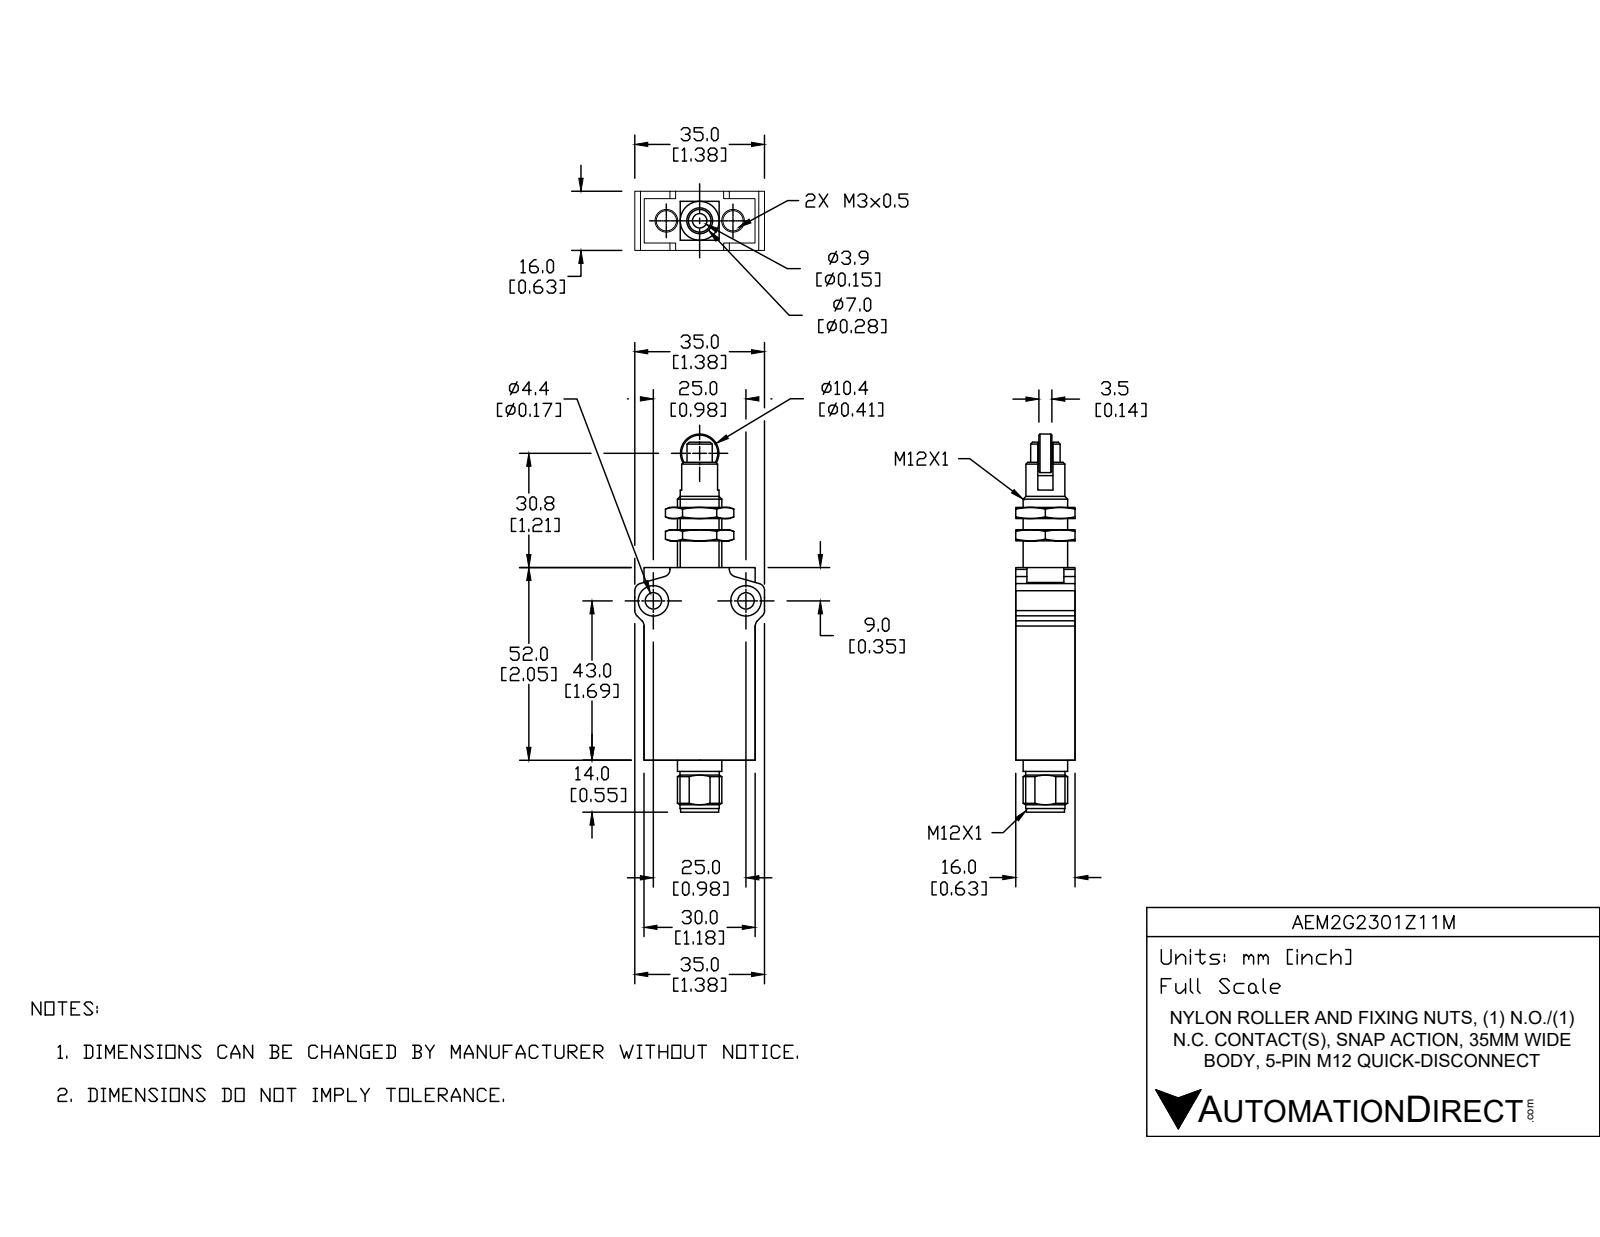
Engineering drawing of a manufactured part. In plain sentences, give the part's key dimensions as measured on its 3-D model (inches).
The part is named "AEM2G2301Z11M". Its 3-D file was written by "SolidWorks 2017 (AUTOMOTIVE_DESIGN)". It is 6 solids with 229 faces: 82 planar, 76 cylindrical and 71 other. Overall it measures 4.016 by 1.378 by 0.63 inches. Its volume is 1.785 cubic inches and its surface area 18.07 square inches. Round holes: 2 of diameter 0.118, 2 of diameter 0.173, 2 of diameter 0.323, 1 of diameter 0.317. Round bosses or shafts: 1 of diameter 0.472, 1 of diameter 0.417, 1 of diameter 0.413, 1 of diameter 0.409, 1 of diameter 0.406, 1 of diameter 0.313, 1 of diameter 0.22. Partial cylindrical surfaces (rounded edges, fillets, slot ends): 8 of radius 0.079, 1 of radius 0.256. The main face-to-face distances are 0.63, 1.181, 0.472, 0.118, 0.236, 2.047, 1.858, 0.189, 0.354, 0.234. The hole center spacings are 0.374, 0.748, 0.984.
